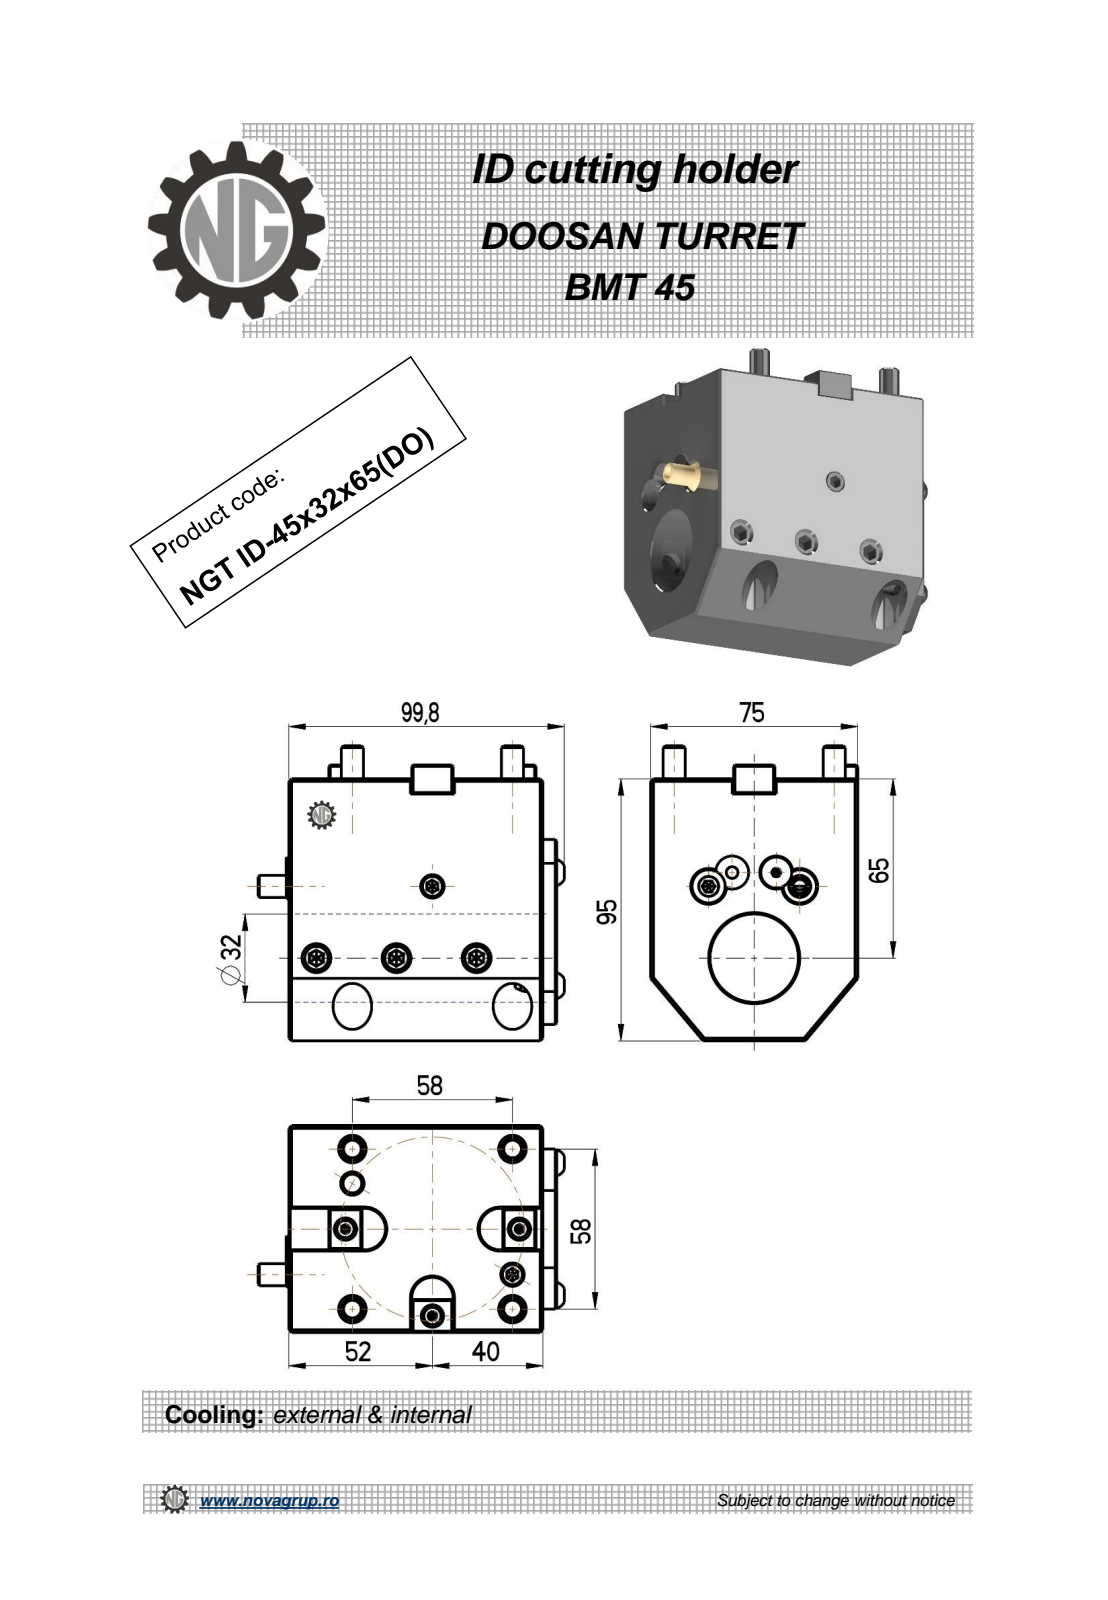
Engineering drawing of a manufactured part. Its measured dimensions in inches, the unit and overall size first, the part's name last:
Units: inches
Overall size (bounding box): 4.365 × 4.213 × 2.953
Round holes (diameter × count): ⌀0.335 ×3, ⌀0.197 ×1, ⌀0.268 ×1, ⌀1.26 ×1
Round bosses / shafts (diameter × count): ⌀0.315 ×5, ⌀0.441 ×1
Partial cylindrical surfaces — rounded edges, fillets, slot ends (radius × count): R0.02 ×36, R0.009 ×6, R0.016 ×6, R0.295 ×3
Main face-to-face distances: 2.953, 0.197, 3.622, 3.74, 3.819, 0.335, 0.472, 1.181, 1.772, 2.283
Hole centre spacings: 1.142, 1.212, 2.283
Volume: 34.09 in³ · Surface area: 90.27 in²
Bodies: 1 solid, 386 faces (194 planar, 93 cylindrical, 99 other)
Part name (STEP PRODUCT): NGT_ID_45_32_65_DO
STEP written by: PRO/ENGINEER BY PARAMETRIC TECHNOLOGY CORPORATION, 2010280 (CONFIG_CONTROL_DESIGN)
